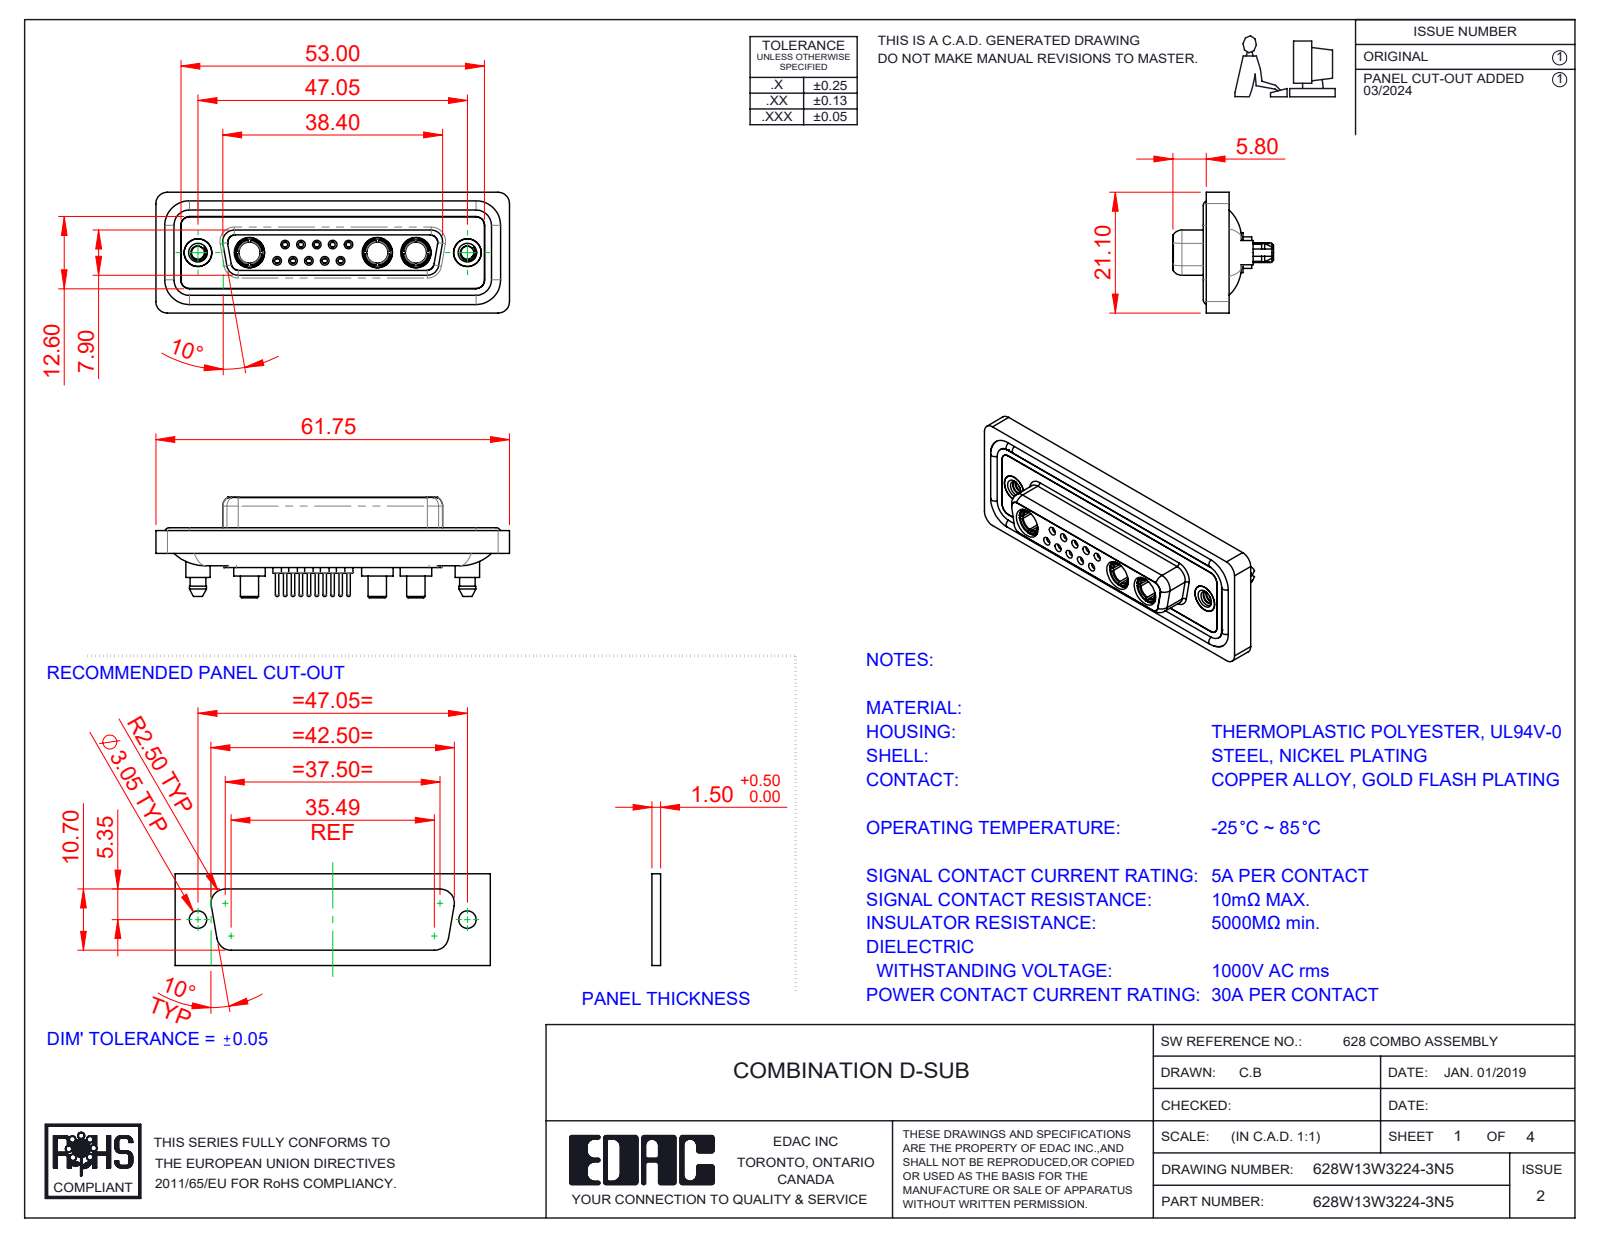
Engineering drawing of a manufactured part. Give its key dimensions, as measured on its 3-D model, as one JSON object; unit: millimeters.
{"part_name": "628Combo Shell Rear_25 Contacts; 628Combo Shell Front_25 Contacts; 628Combo Contact Row 1_24; 628Combo Contact Row 2_24 (+5 more)", "step_written_by": "SolidWorks 2023 (CONFIG_CONTROL_DESIGN)", "units": "millimeters", "bodies": {"solids": 23, "faces": 1208, "planar": 358, "cylindrical": 479, "other": 371}, "overall_size": [61.75, 21.1, 17.55], "volume_mm3": 8428, "surface_area_mm2": 14055, "round_holes": [[0.9, 10], [1.1, 10], [1.5, 10], [2, 10], [1.6, 5], [1.7, 5], [4.85, 5], [3.7, 3], [5.3, 3], [2.26, 2], [4, 2], [4.05, 2]], "round_bosses_or_shafts": [[2.2, 10], [0.6, 10], [1.6, 9], [5.5, 3], [5.2, 3], [4.96, 3], [4.75, 3], [3.75, 3]], "partial_cylinders_radius": [[1.5, 24], [2, 18], [1.6, 10], [1.35, 8], [0.25, 4], [0.5, 4], [0.6, 4], [0.65, 4]], "face_to_face_distances": [0.4, 1.8, 7.45, 5.65, 0.5, 6.6, 7.05, 1.6, 2.9, 1.1], "hole_center_spacings": [3.16, 2.77, 5.03, 5.04, 5.54, 8.31, 7.49, 2.76]}
